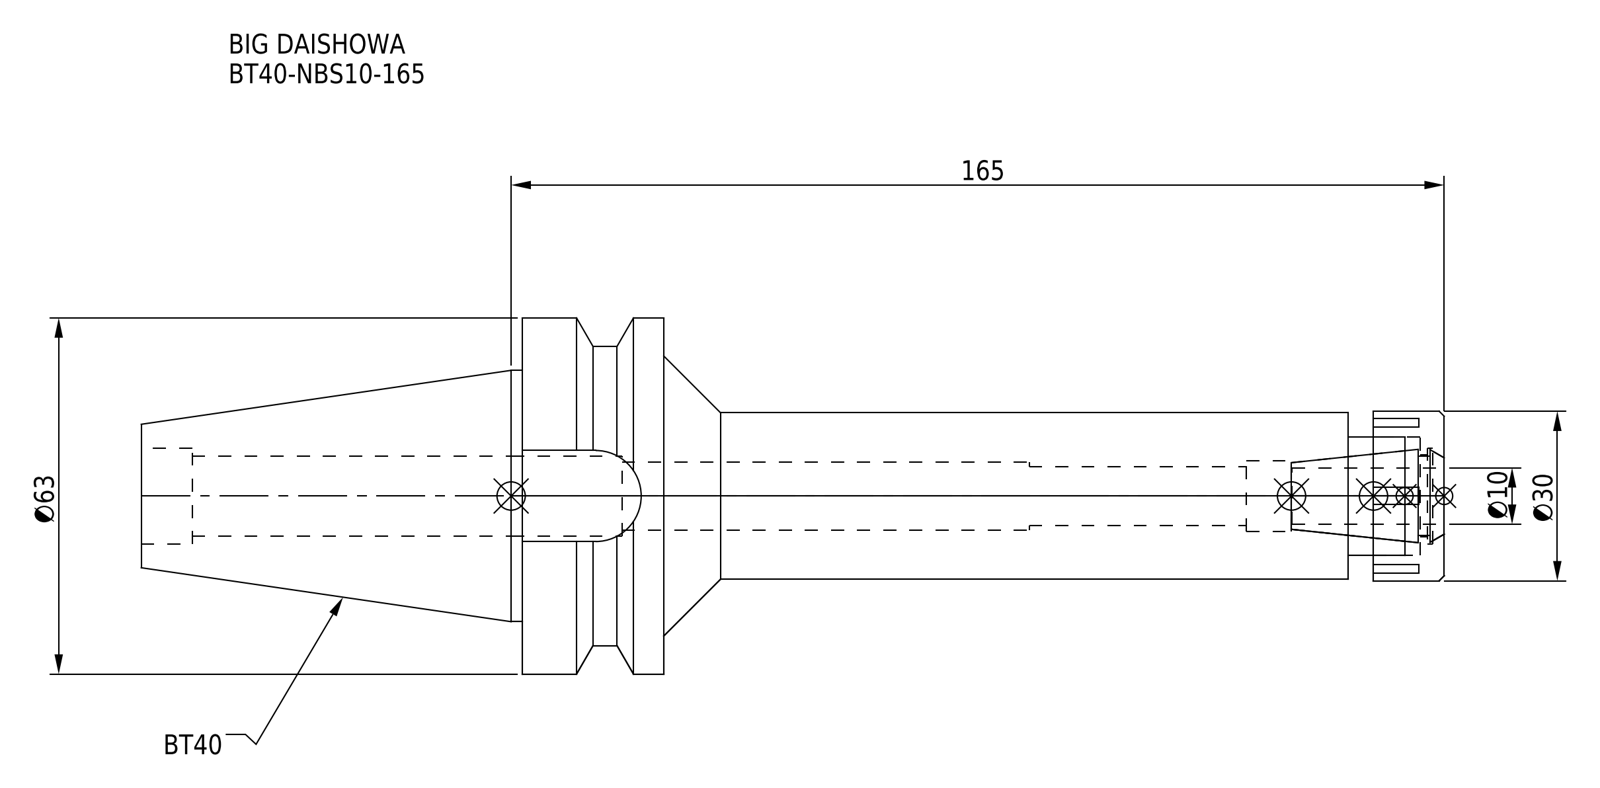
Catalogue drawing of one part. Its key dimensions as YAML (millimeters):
part_name: "BT40-NBS10-165; BT40-NBS10-165_1.stp; DXF_TEMP_ASSY_ASM_4_ASM.stp; BT40-NBS10-165.stp (+3 more)"
step_written_by: "SolidWorks 2019 (CONFIG_CONTROL_DESIGN)"
units: millimeters
bodies: {solids: 2, faces: 93, planar: 45, cylindrical: 34, other: 14}
overall_size: [230.4, 63, 63]
volume: 201511
surface_area: 42250
round_holes:
  - {diameter: 10.4, count: 1}
  - {diameter: 12, count: 1}
  - {diameter: 12.5, count: 1}
  - {diameter: 14.2, count: 1}
  - {diameter: 14.5, count: 1}
  - {diameter: 17, count: 1}
  - {diameter: 21, count: 1}
round_bosses_or_shafts:
  - {diameter: 63, count: 1}
  - {diameter: 53, count: 1}
  - {diameter: 44.45, count: 1}
  - {diameter: 30, count: 1}
  - {diameter: 29.5, count: 1}
partial_cylinders:
  - {radius: 8.05, count: 1}
face_to_face_distances: [25, 138, 163, 4.5, 12.5, 17, 121, 146, 125.5, 150.5]
